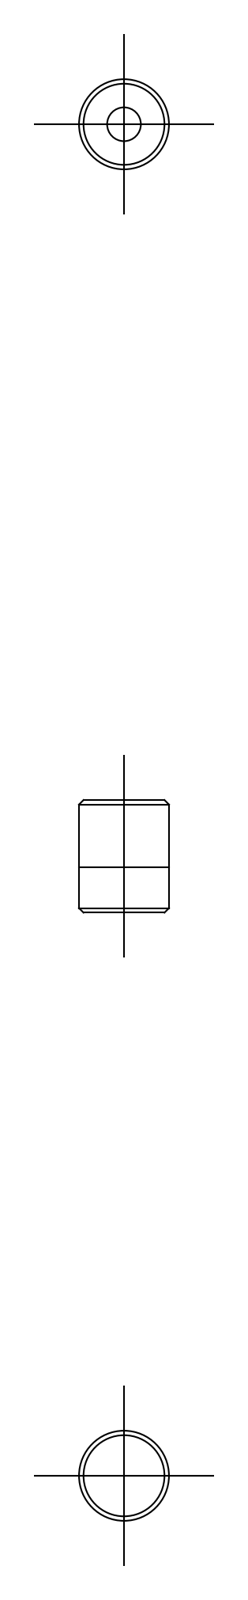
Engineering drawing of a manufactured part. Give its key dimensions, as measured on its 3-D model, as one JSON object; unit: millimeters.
{"step_written_by": "CADfix (AUTOMOTIVE_DESIGN)", "units": "millimeters", "bodies": {"solids": 1, "faces": 16, "planar": 0, "cylindrical": 0, "other": 16}, "overall_size": [5, 4, 4], "volume_mm3": 62, "surface_area_mm2": 90}
